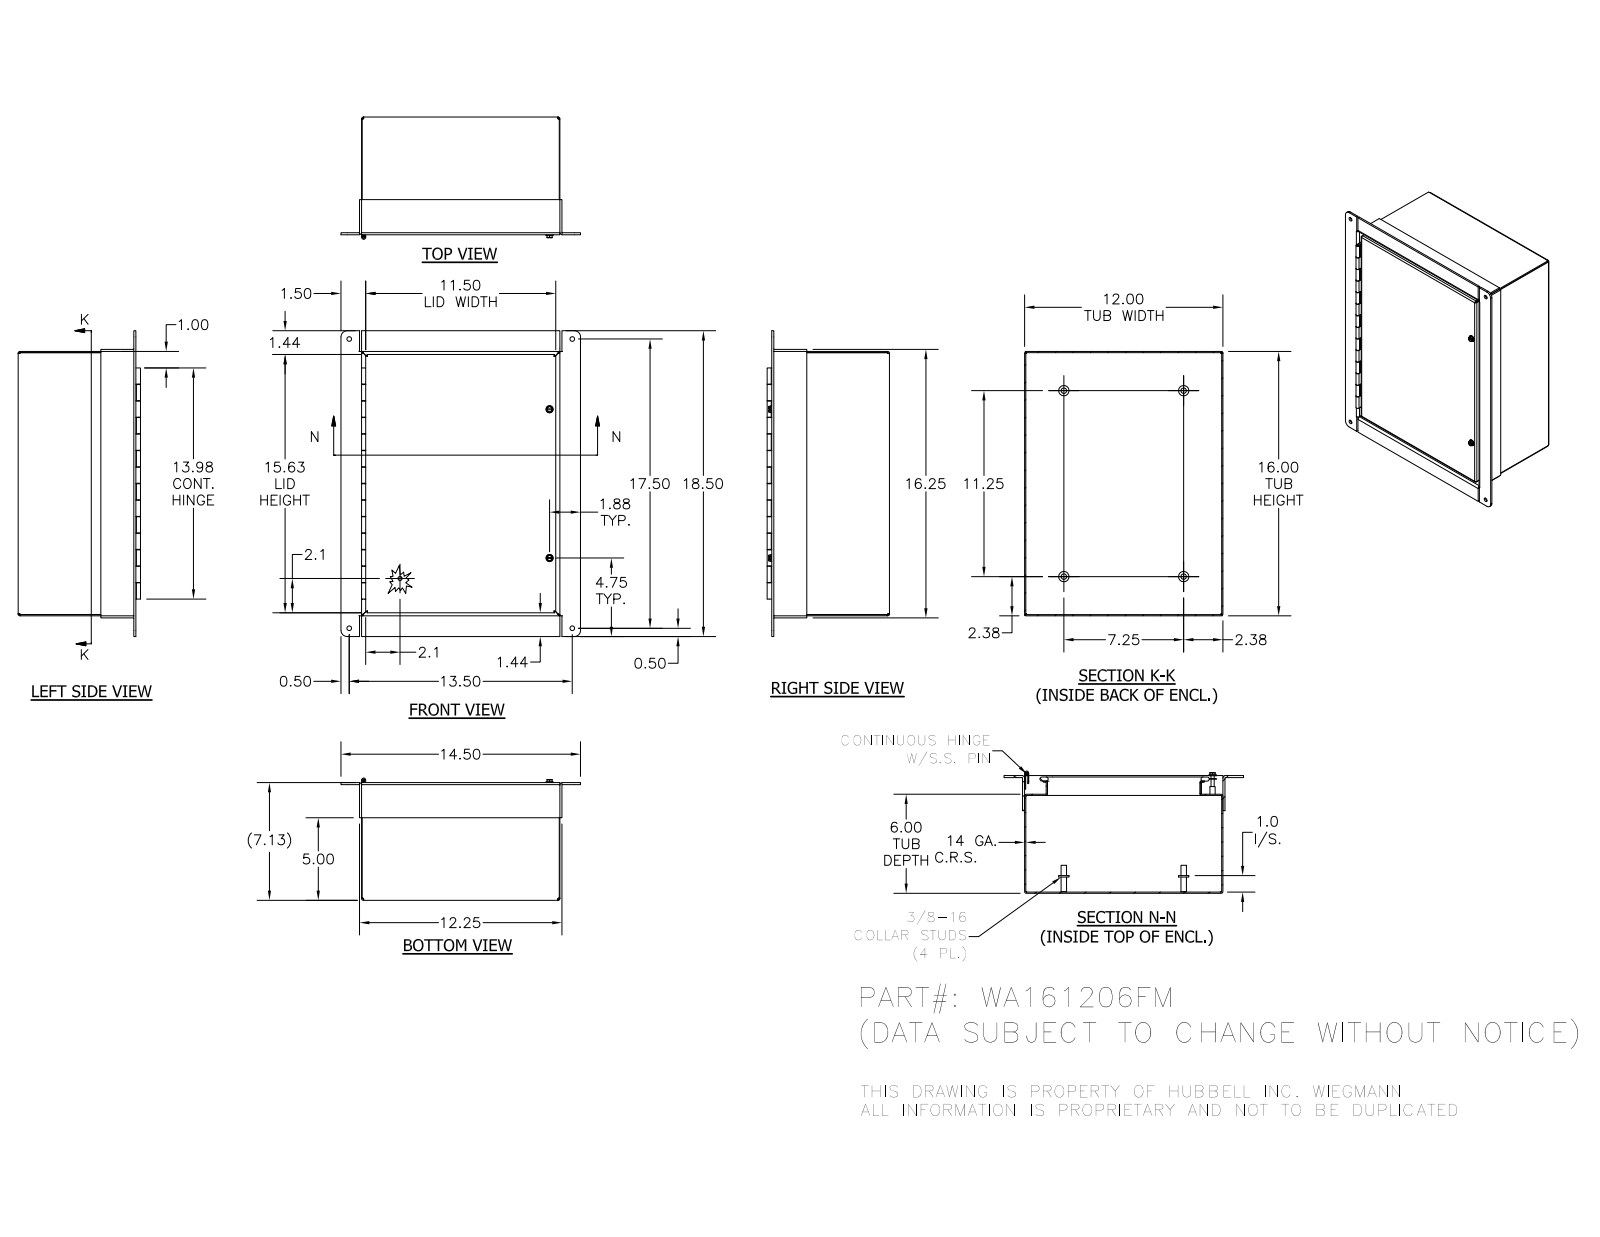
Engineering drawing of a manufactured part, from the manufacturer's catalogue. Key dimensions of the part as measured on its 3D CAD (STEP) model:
Part name (STEP PRODUCT): WA161206FMBKP; WA1612FMLID; 388116; H6010100T-14 (+8 more)
STEP written by: Autodesk Inventor 2014 (AUTOMOTIVE_DESIGN)
Units: millimetres
Bodies: 23 solids, 568 faces (347 planar, 150 cylindrical, 71 other)
Overall size (bounding box): 469.9 × 368.3 × 187.96
Volume: 1 529 000 mm³ · Surface area: 1 435 000 mm²
Round holes (diameter × count): ⌀7.14 ×6, ⌀9.52 ×3, ⌀3.96 ×2, ⌀4.78 ×2, ⌀7.06 ×2, ⌀3.17 ×1
Round bosses / shafts (diameter × count): ⌀15.88 ×4, ⌀8.38 ×4, ⌀11.51 ×2, ⌀11.11 ×2, ⌀10.52 ×2, ⌀7.94 ×2, ⌀6.35 ×2, ⌀4.83 ×2
Partial cylindrical surfaces — rounded edges, fillets, slot ends (radius × count): R0.79 ×24, R2.67 ×20, R1.78 ×8, R3.17 ×8, R3.97 ×4, R9.53 ×4, R2.27 ×2
Main face-to-face distances: 1.88, 178.84, 176.96, 302.92, 180.72, 3.17, 404.52, 304.8, 150.52, 28.32
Hole centre spacings: 113.46, 143.94, 326.35, 338.36, 342.9, 444.5, 456.2, 561.39
